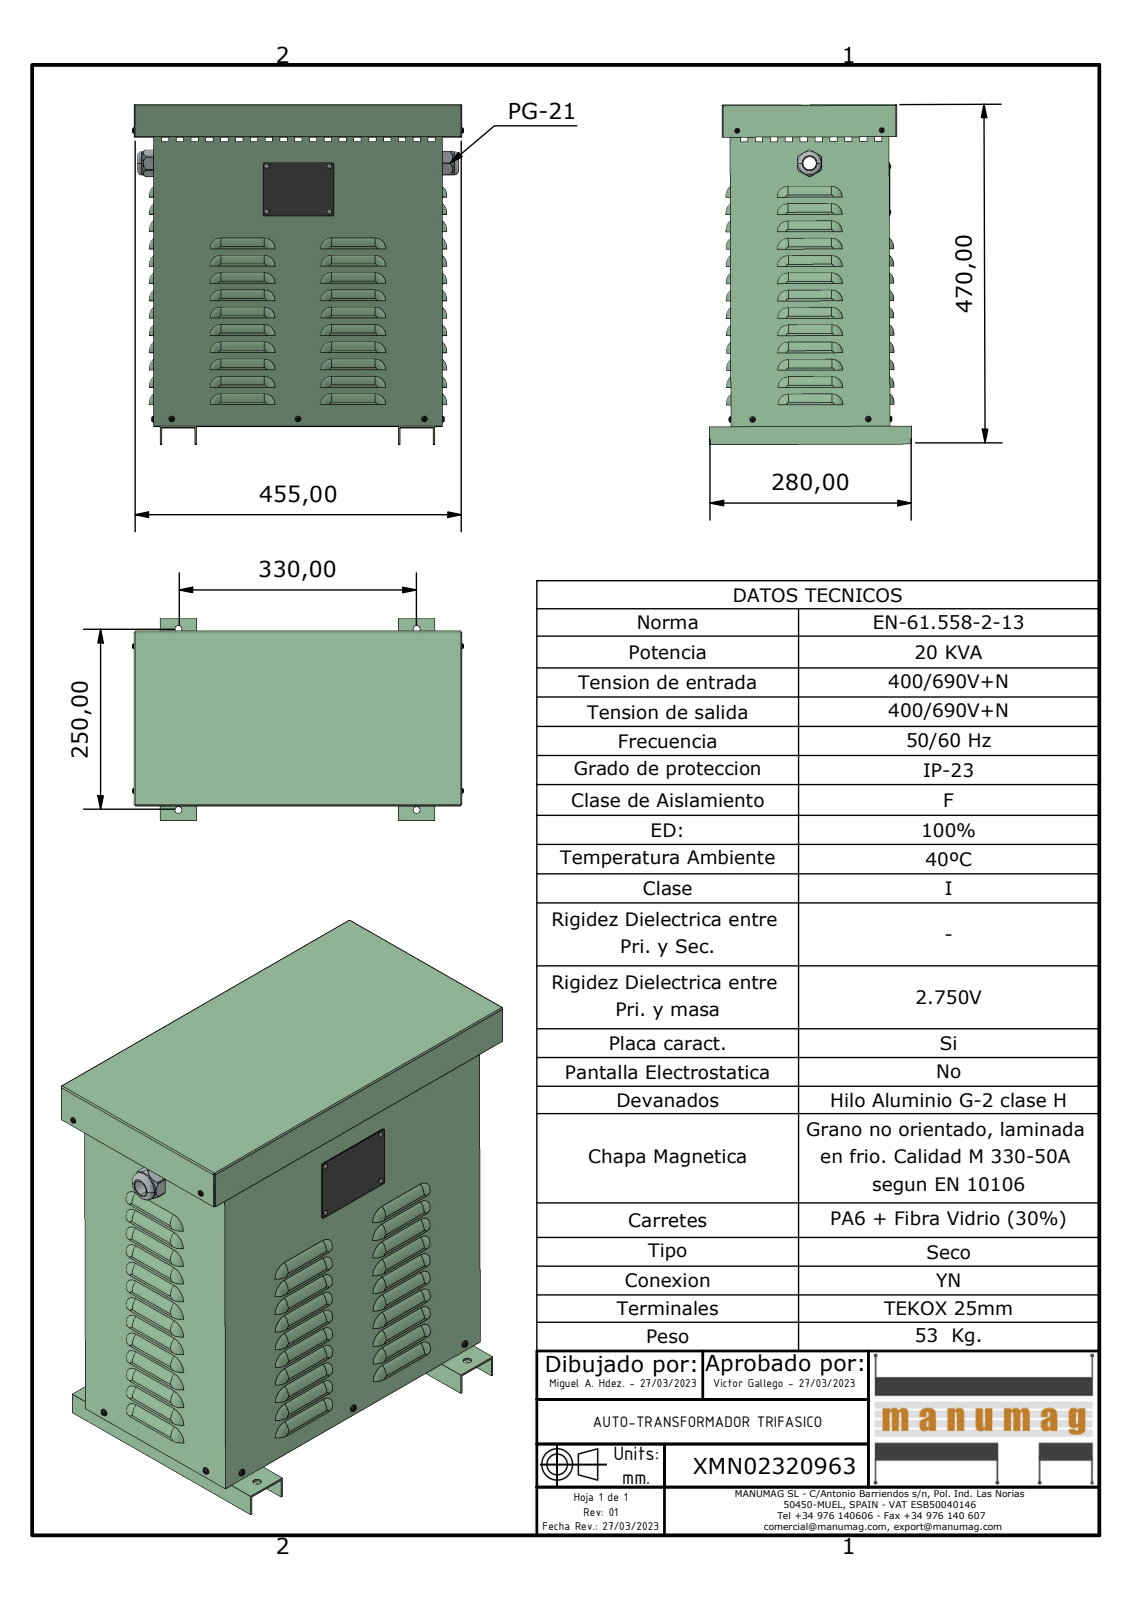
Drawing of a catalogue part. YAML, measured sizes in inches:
part_name: "XMN02320963; JE015 - JE020 - JE025 NACIONAL CUERPO; JE015 - JE020 - JE025 NACIONAL BASE; JE015 - JE020 - JE025 NACIONAL PATA (+6 more)"
step_written_by: "Autodesk Inventor 2023 (AUTOMOTIVE_DESIGN)"
units: inches
bodies: {solids: 26, faces: 2110, planar: 1086, cylindrical: 450, other: 574}
overall_size: [18.596, 18.076, 11.027]
volume: 101
surface_area: 2761
round_holes:
  - {diameter: 0.177, count: 12}
  - {diameter: 0.157, count: 6}
  - {diameter: 0.378, count: 4}
  - {diameter: 0.709, count: 1}
  - {diameter: 1.181, count: 1}
round_bosses_or_shafts:
  - {diameter: 0.157, count: 8}
  - {diameter: 0.143, count: 8}
  - {diameter: 0.126, count: 4}
  - {diameter: 0.138, count: 2}
  - {diameter: 0.125, count: 2}
  - {diameter: 1.276, count: 1}
  - {diameter: 1.122, count: 1}
  - {diameter: 1.114, count: 1}
partial_cylinders:
  - {radius: 0.551, count: 118}
  - {radius: 0.157, count: 49}
  - {radius: 0.591, count: 49}
  - {radius: 0.118, count: 16}
  - {radius: 0.177, count: 16}
  - {radius: 0.059, count: 8}
  - {radius: 0.079, count: 4}
  - {radius: 0.732, count: 1}
face_to_face_distances: [0.059, 8.602, 8.543, 17.52, 15.689, 8.661, 15.63, 17.579, 15.748, 17.461]
hole_center_spacings: [6.89, 2.48, 13.78, 0.02, 3.425, 3.445, 4.229, 4.245]
